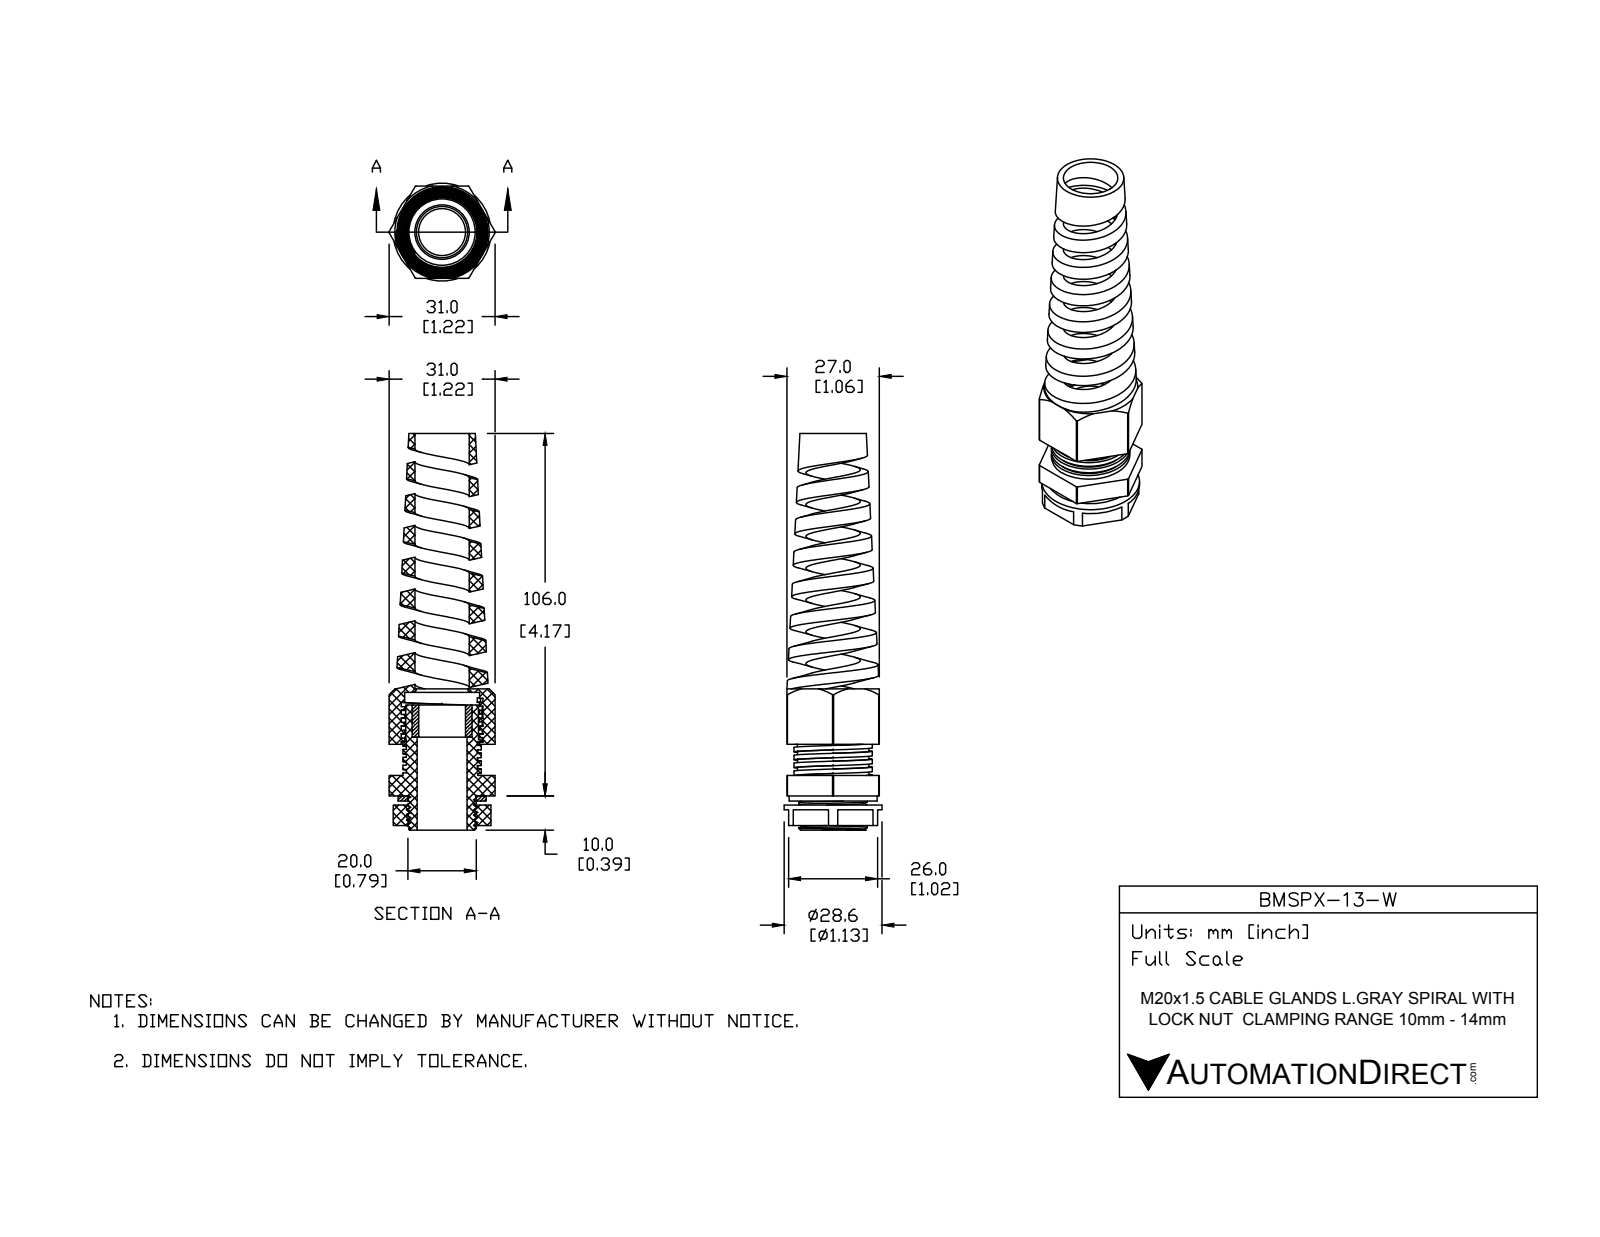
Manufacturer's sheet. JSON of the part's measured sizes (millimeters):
{"part_name": "BMSPX-13-W", "step_written_by": "SolidWorks 2015 (CONFIG_CONTROL_DESIGN)", "units": "millimeters", "bodies": {"solids": 5, "faces": 239, "planar": 104, "cylindrical": 94, "other": 41}, "overall_size": [116, 31, 28.6], "volume_mm3": 22734, "surface_area_mm2": 22760, "round_holes": [[13.7, 1], [14.6, 1], [15.9, 1], [17.5, 1], [19.18, 1], [19.8, 1], [21.9, 1]], "round_bosses_or_shafts": [[28.6, 1], [25.75, 1], [22.9, 1], [21.3, 1], [20, 1]], "partial_cylinders_radius": [[15.5, 1]], "face_to_face_distances": [27, 0.5, 6, 8.65, 2.65, 26.5, 14.65, 39.95, 33.95, 31.3]}
